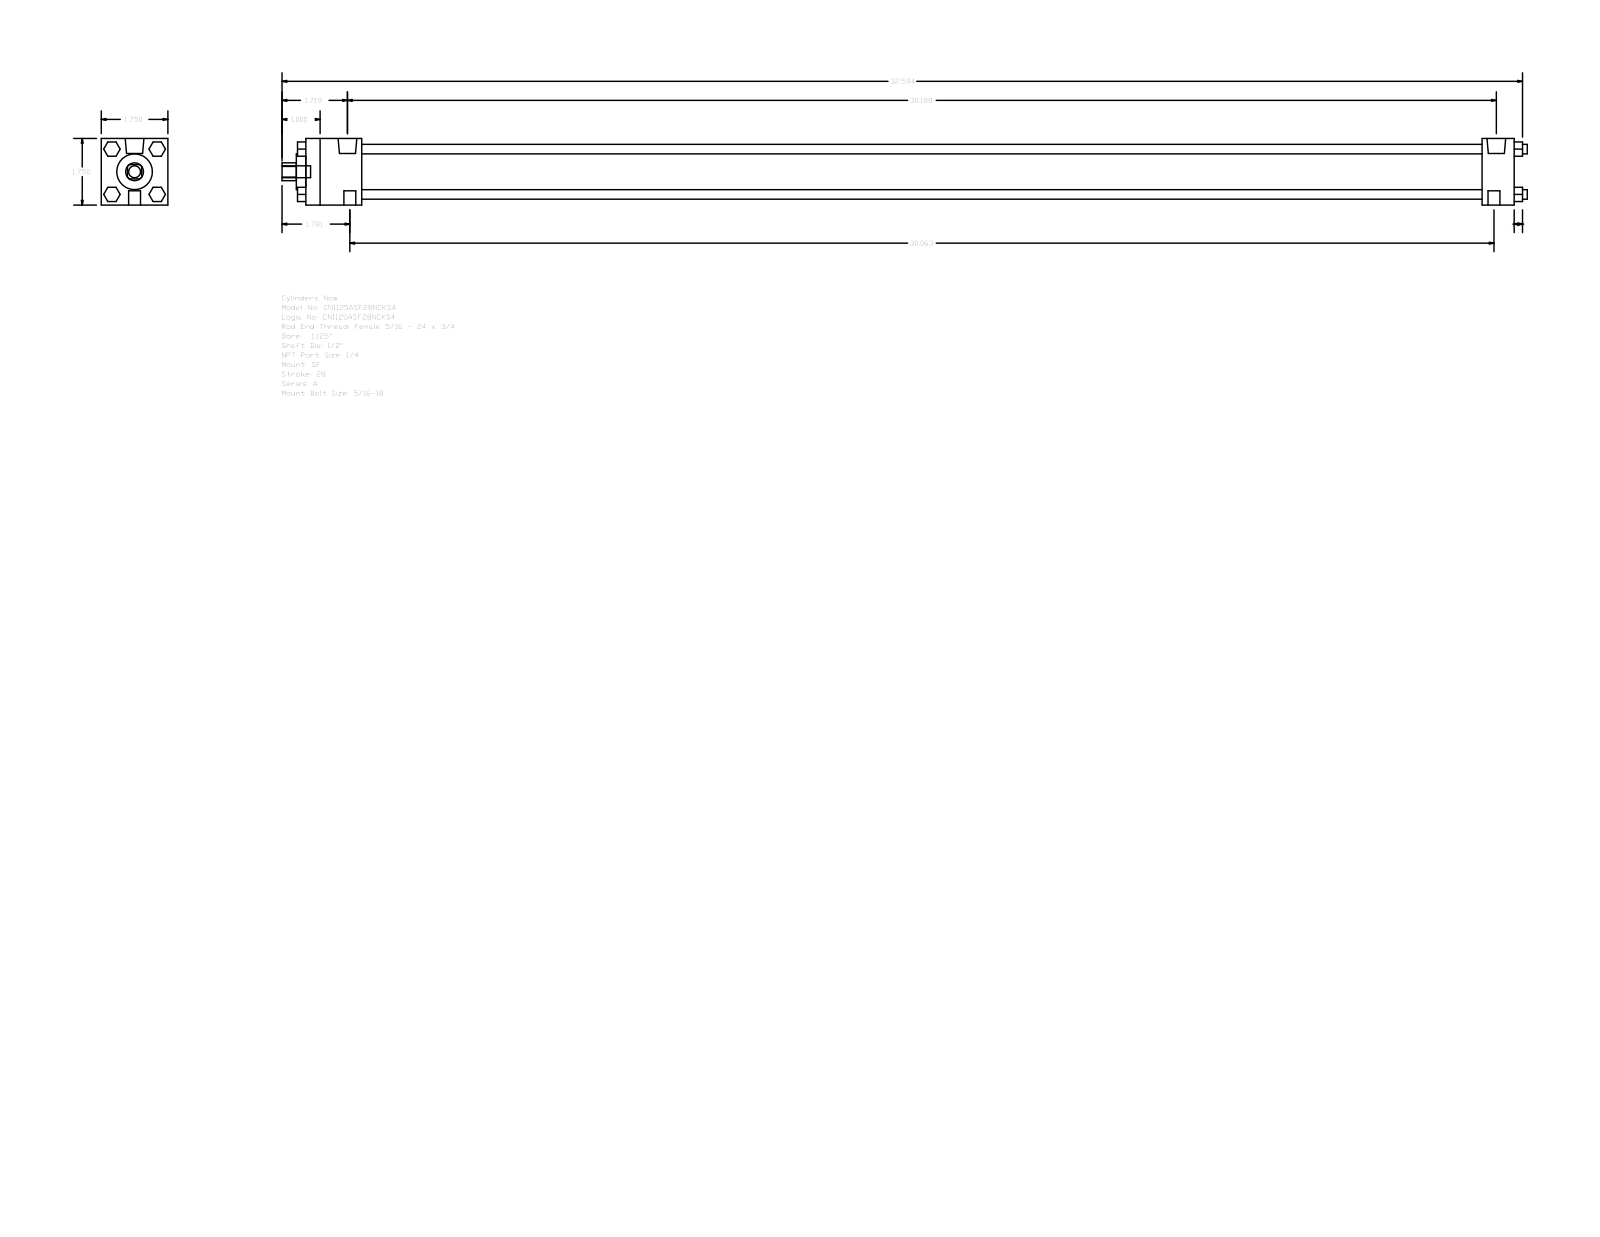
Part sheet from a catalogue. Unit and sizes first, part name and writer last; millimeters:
Units: millimetres
Overall size (bounding box): 831.06 × 44.45 × 44.45
Round holes (diameter × count): ⌀12.7 ×1, ⌀23.81 ×1, ⌀31.88 ×1
Round bosses / shafts (diameter × count): ⌀6.35 ×4, ⌀7.94 ×3, ⌀12.49 ×2, ⌀5.56 ×2
Partial cylindrical surfaces — rounded edges, fillets, slot ends (radius × count): R5.94 ×1
Main face-to-face distances: 44.46, 806.45, 785.01, 21.44, 37.3, 747.71, 769.15, 9.53, 5.59, 9.52
Bodies: 0 solids, 120 faces (92 planar, 28 cylindrical, 0 other)
Part name (STEP PRODUCT): A_SF__0112_0.5
STEP written by: GSSL Pune (CONFIG_CONTROL_DESIGN)
